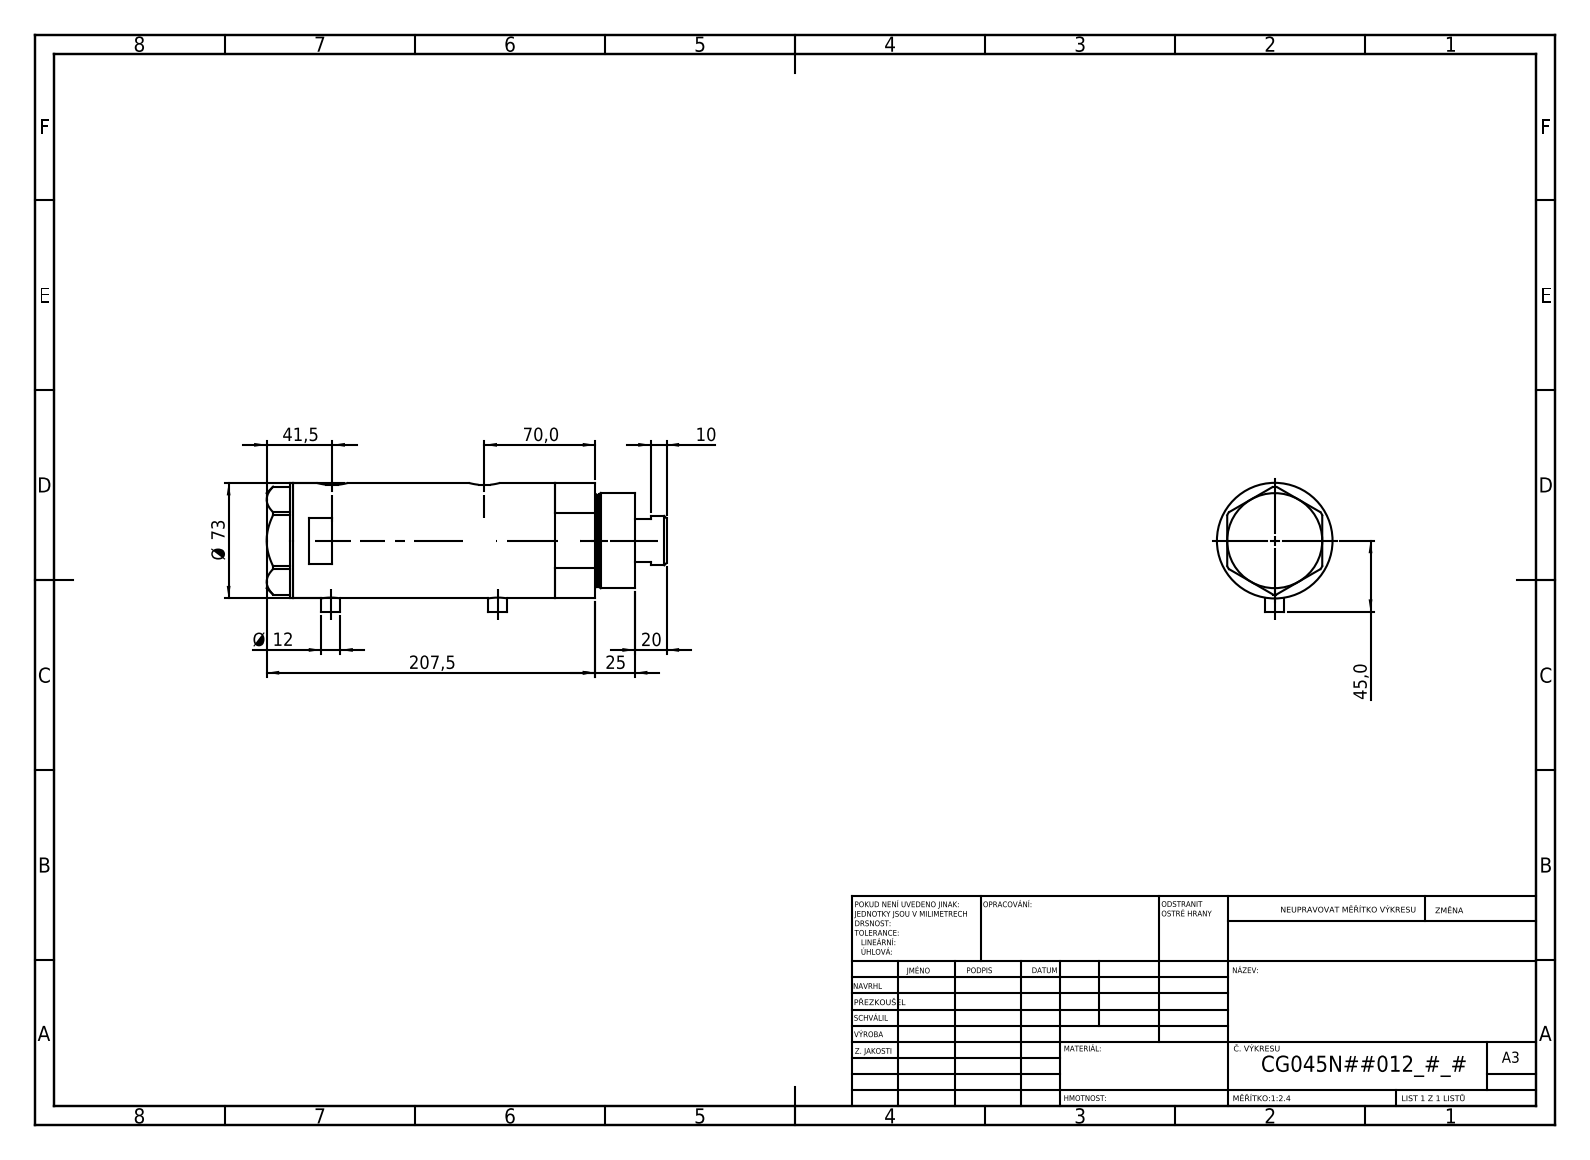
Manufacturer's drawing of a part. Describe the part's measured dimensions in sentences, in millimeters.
The part is named "V270CG_MIDDLE; V270CG_VC; V270CG_FRONT; V270CG_BACK". Its 3-D file was written by "SolidWorks 2019 (CONFIG_CONTROL_DESIGN)". It is 4 solids with 120 faces: 49 planar, 51 cylindrical and 20 other. Overall it measures 252.5 by 81.5 by 73 millimeters. Its volume is 916 019 cubic millimeters and its surface area 150 503 square millimeters. Round holes: 2 of diameter 12.5, 2 of diameter 13.16, 1 of diameter 10.5, 1 of diameter 32, 1 of diameter 33.5, 1 of diameter 45, 1 of diameter 48, 1 of diameter 64. Round bosses or shafts: 2 of diameter 12, 1 of diameter 73, 1 of diameter 60, 1 of diameter 58, 1 of diameter 31. Partial cylindrical surfaces (rounded edges, fillets, slot ends): 2 of radius 10. The main face-to-face distances are 95, 121, 26, 16.5, 42.5, 137.5, 2, 216, 232.5, 190. The hole center spacings are 1, 8.5, 96, 97, 104.5, 105.5.
